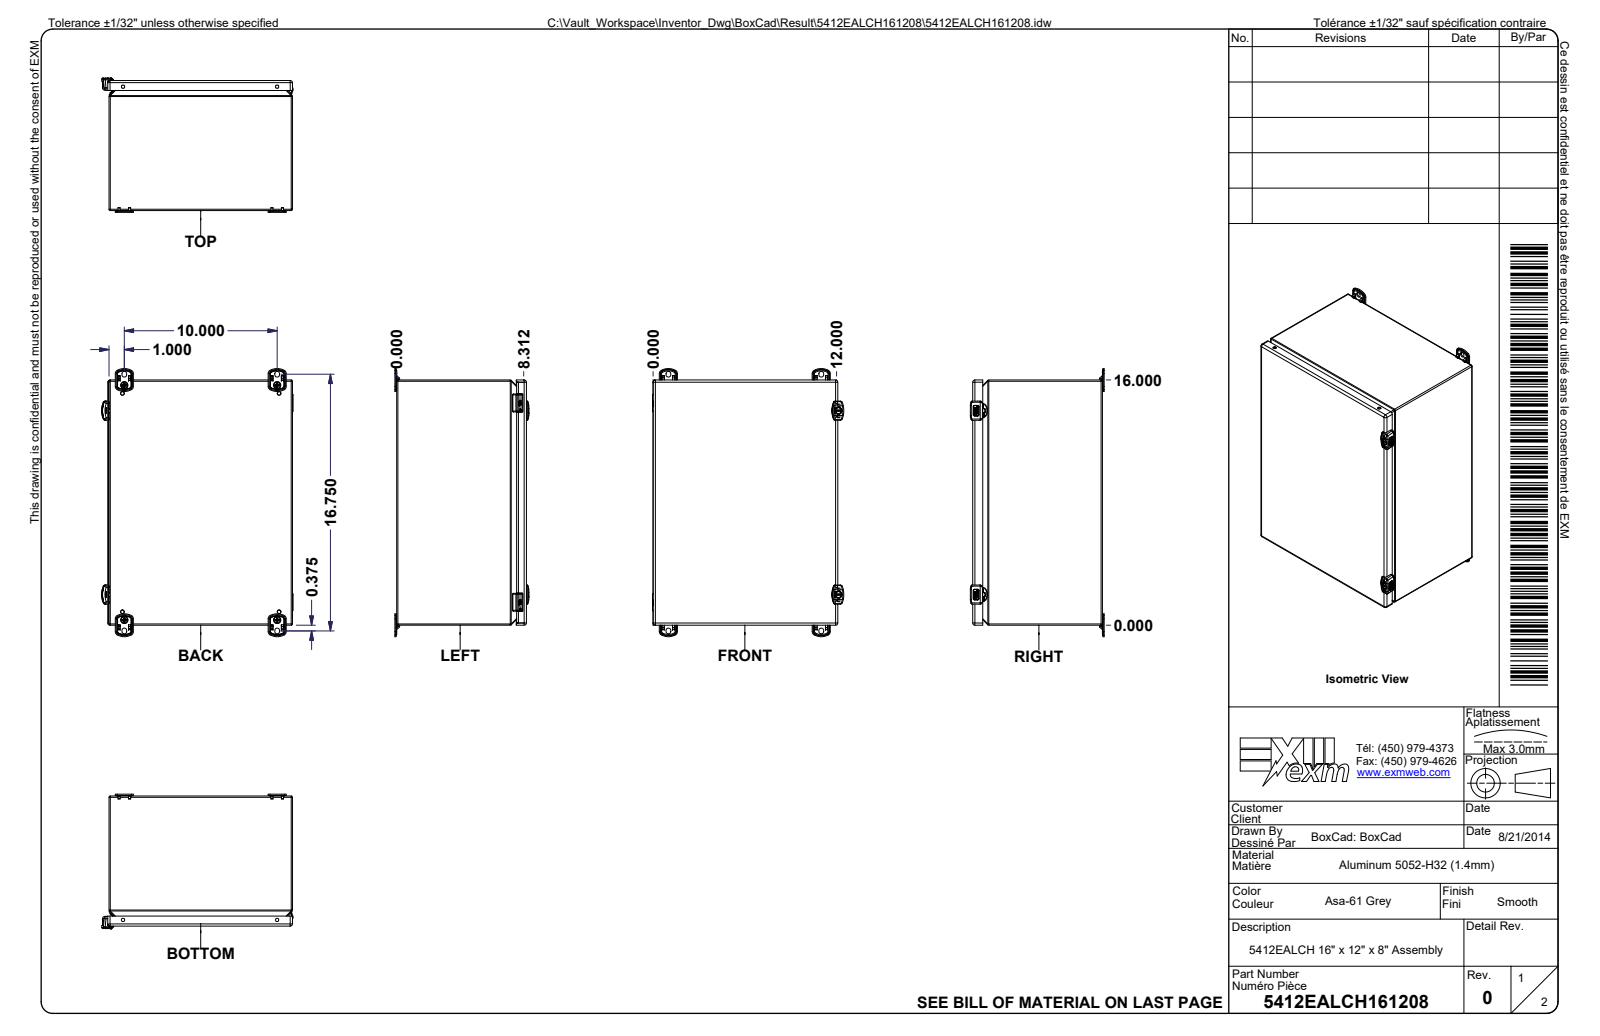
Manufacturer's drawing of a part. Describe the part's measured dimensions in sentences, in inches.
The part is named "5412EALCH161208; 5412EALCH161208B; 5412EALCH161208B-P; STK-A-70469-1 (+8 more)". Its 3-D file was written by "Autodesk Inventor 2020 (AUTOMOTIVE_DESIGN)". It is 59 solids with 8409 faces: 3583 planar, 2002 cylindrical and 2824 other. Overall it measures 17.496 by 12.503 by 8.76 inches. Its volume is 63.19 cubic inches and its surface area 2 257 square inches. Round holes: 4 of diameter 0.165, 4 of diameter 0.173, 4 of diameter 0.197, 4 of diameter 0.197, 4 of diameter 0.236, 4 of diameter 0.236, 4 of diameter 0.32, 2 of diameter 0.03, 2 of diameter 0.175, 2 of diameter 0.201, 2 of diameter 0.24, 2 of diameter 0.339. Round bosses or shafts: 8 of diameter 0.232, 4 of diameter 0.5, 4 of diameter 0.3, 4 of diameter 0.236, 4 of diameter 0.193, 3 of diameter 0.197, 2 of diameter 0.412, 2 of diameter 0.394. Partial cylindrical surfaces (rounded edges, fillets, slot ends): 257 of radius 0.02, 209 of radius 0.01, 92 of radius 0.039, 64 of radius 0.004, 60 of radius 0.008, 57 of radius 0.059, 35 of radius 0.031, 33 of radius 0.005. The main face-to-face distances are 0.053, 11.947, 0.053, 8.433, 8.38, 15.947, 8.486, 8.433, 0.304, 0.236. The hole center spacings are 0.546, 10.139, 14.781, 17.916, 1.507, 10.25, 10.25, 13.163.
